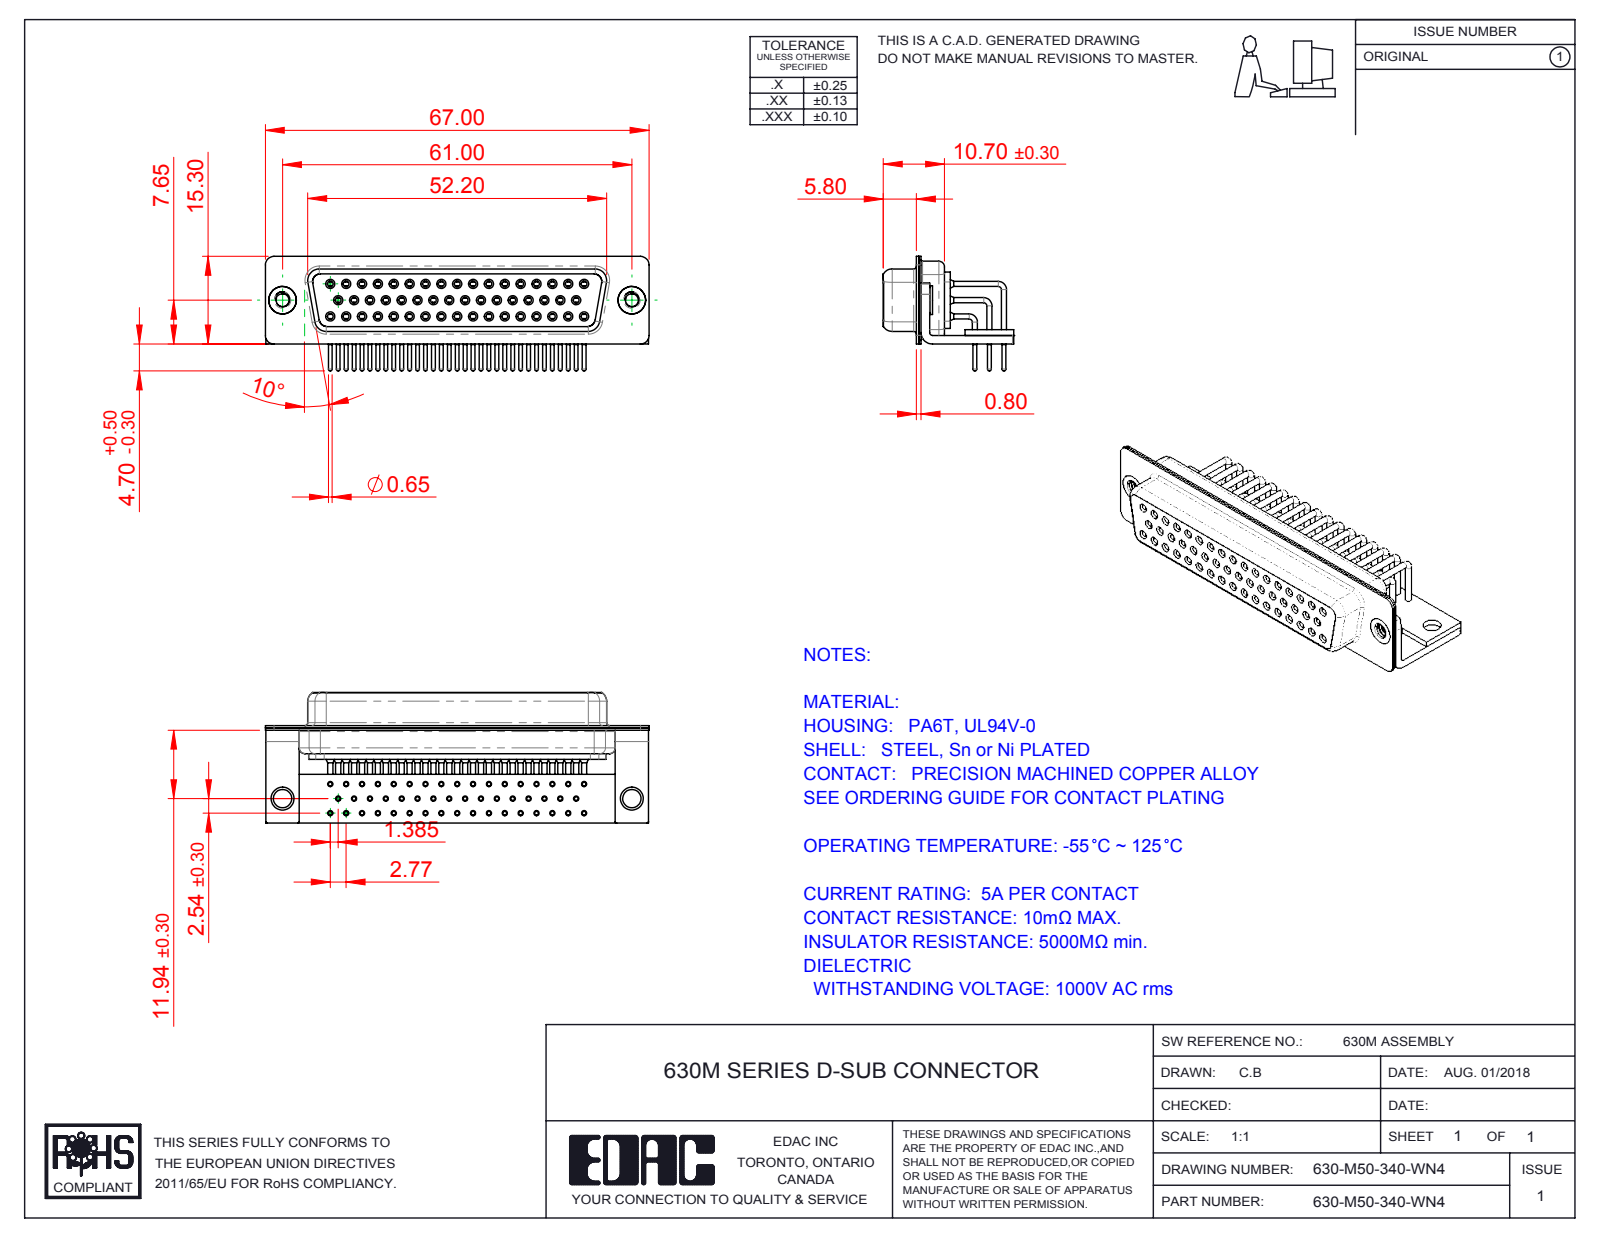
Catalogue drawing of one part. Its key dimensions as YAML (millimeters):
part_name: "630M 4-40 Threaded Rivet_Stabilizer; 630M Stabilizer Board_50 Contacts; 630M Housing_50 Contacts; 630M Shell Rear_50 Contacts (+6 more)"
step_written_by: "SolidWorks 2016 (CONFIG_CONTROL_DESIGN)"
units: millimeters
bodies: {solids: 58, faces: 3079, planar: 843, cylindrical: 1409, other: 827}
overall_size: [67, 22.8, 20]
volume: 7864
surface_area: 18601
round_holes:
  - {diameter: 0.9, count: 50}
  - {diameter: 1, count: 50}
  - {diameter: 1.1, count: 50}
  - {diameter: 1.7, count: 50}
  - {diameter: 1.8, count: 50}
  - {diameter: 2, count: 50}
  - {diameter: 2.26, count: 2}
  - {diameter: 3.2, count: 2}
  - {diameter: 4, count: 2}
  - {diameter: 4.8, count: 2}
round_bosses_or_shafts:
  - {diameter: 0.9, count: 59}
  - {diameter: 1.6, count: 50}
  - {diameter: 1.5, count: 50}
  - {diameter: 0.65, count: 50}
  - {diameter: 5, count: 2}
  - {diameter: 4.9, count: 2}
partial_cylinders:
  - {radius: 0.25, count: 16}
  - {radius: 1.5, count: 16}
  - {radius: 2, count: 13}
  - {radius: 1.35, count: 8}
  - {radius: 1.6, count: 8}
  - {radius: 0.5, count: 5}
  - {radius: 0.6, count: 4}
  - {radius: 0.65, count: 4}
face_to_face_distances: [0.4, 1, 2.2, 0.85, 1.35, 11.85, 12.25, 5.8, 5.9, 0.8]
hole_center_spacings: [2.77, 5.54, 8.31, 11.08, 13.85, 16.62, 3.16, 19.39]
